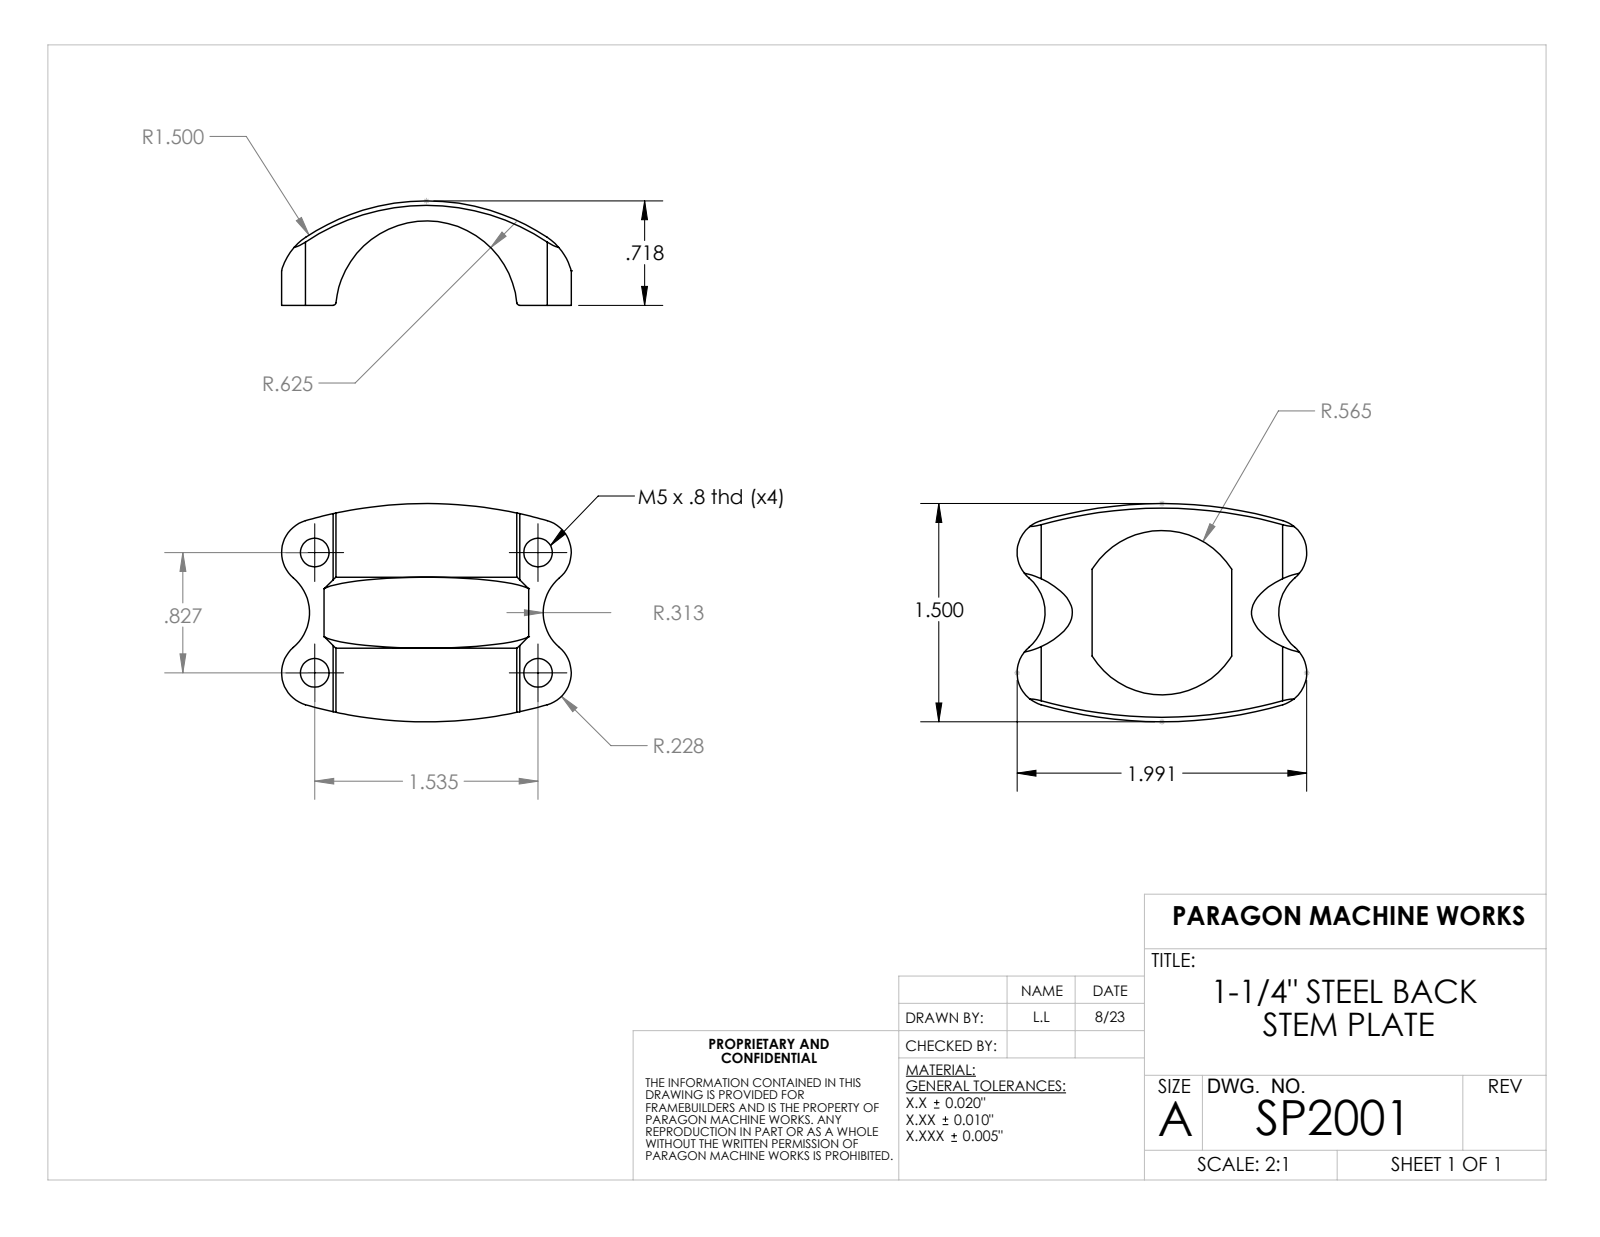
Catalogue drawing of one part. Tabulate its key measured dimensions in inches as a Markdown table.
| quantity | value |
| --- | --- |
| part name | SP2001 |
| STEP written by | SolidWorks 2012 (CONFIG_CONTROL_DESIGN) |
| units | inches |
| bodies | 1 solid, 43 faces (7 planar, 26 cylindrical, 10 other) |
| overall size | 1.991 × 1.5 × 0.718 |
| volume | 0.633 in³ |
| surface area | 9.565 in² |
| round holes (diameter × count) | 0.197 × 4 |
| partial cylindrical surfaces (radius × count) | 0.228 × 4, 0.02 × 2, 0.313 × 2, 0.4 × 2, 2.992 × 2, 0.565 × 1, 0.625 × 1, 0.717 × 1 |
| main face-to-face distances | 0.639, 0.331 |
| hole center spacings | 0.827, 1.535, 1.744 |
